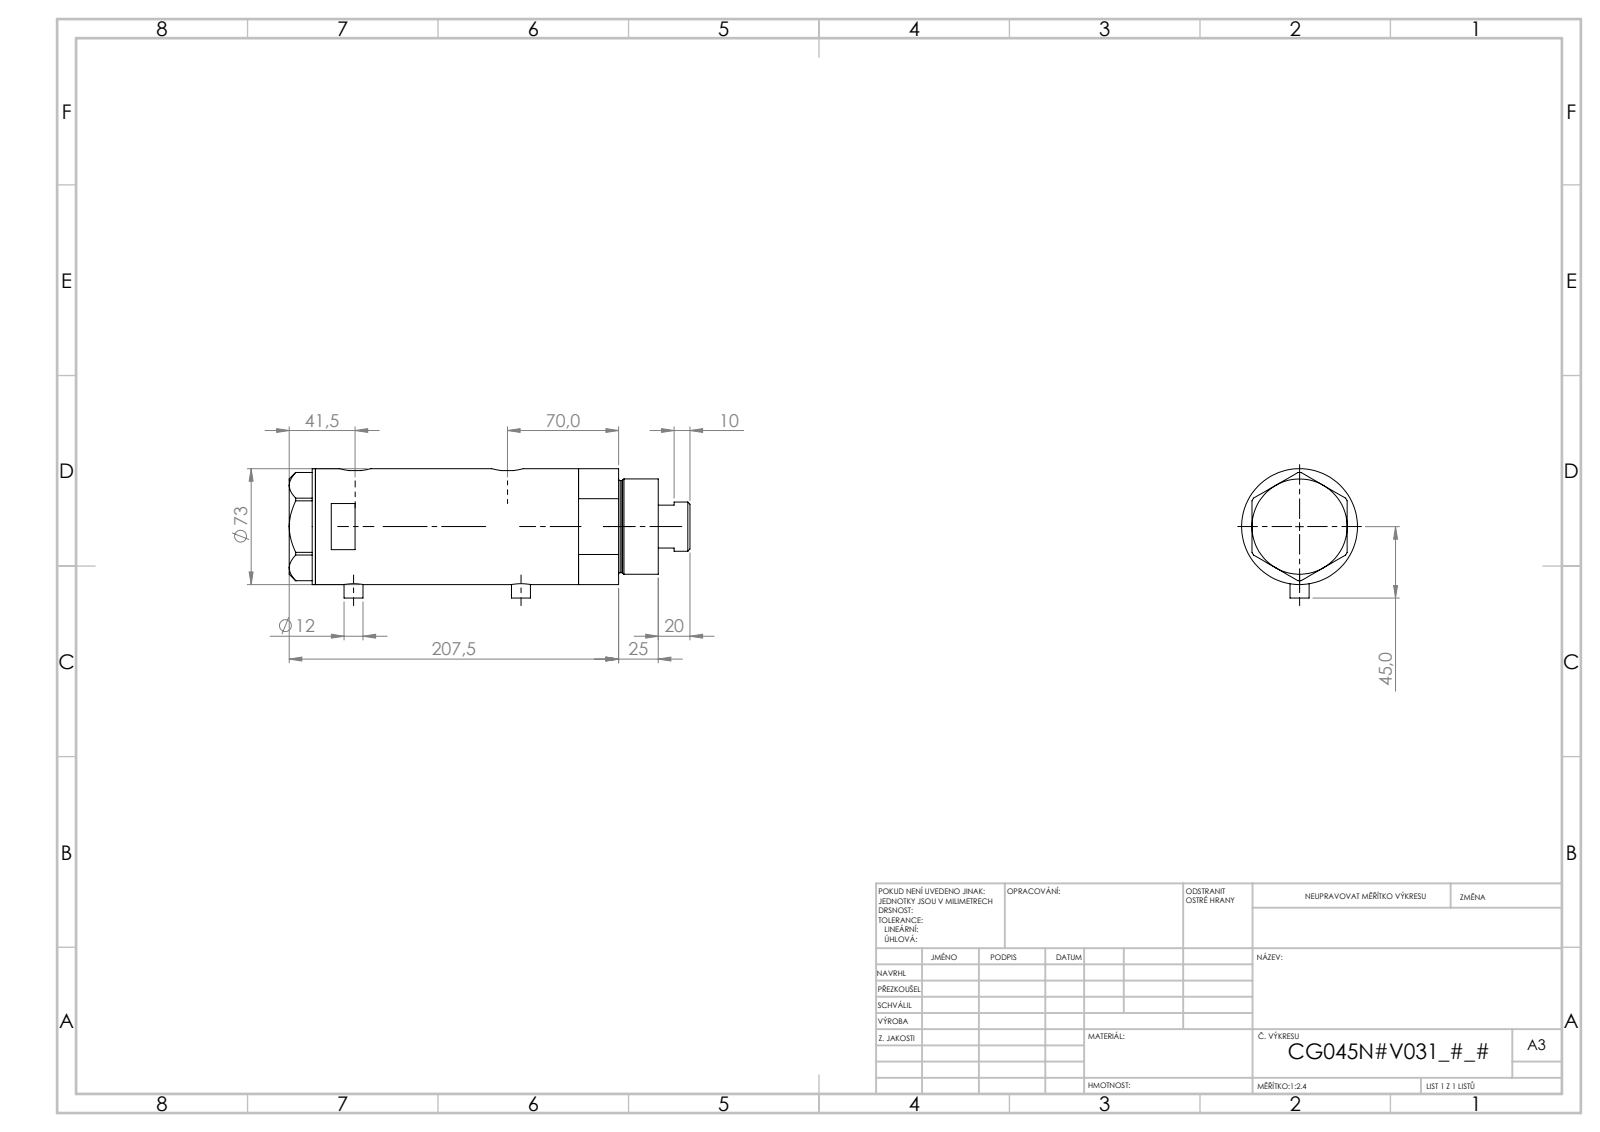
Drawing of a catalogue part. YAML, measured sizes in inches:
part_name: "V270CG_VC; V270CG_MIDDLE; V270CG_FRONT; V270CG_BACK"
step_written_by: "SolidWorks 2019 (CONFIG_CONTROL_DESIGN)"
units: inches
bodies: {solids: 4, faces: 120, planar: 49, cylindrical: 51, other: 20}
overall_size: [9.941, 3.209, 2.874]
volume: 54.8
surface_area: 231.8
round_holes:
  - {diameter: 0.492, count: 2}
  - {diameter: 0.518, count: 2}
  - {diameter: 0.413, count: 1}
  - {diameter: 1.26, count: 1}
  - {diameter: 1.319, count: 1}
  - {diameter: 1.772, count: 1}
  - {diameter: 1.89, count: 1}
  - {diameter: 2.52, count: 1}
round_bosses_or_shafts:
  - {diameter: 0.472, count: 2}
  - {diameter: 2.874, count: 1}
  - {diameter: 2.362, count: 1}
  - {diameter: 2.283, count: 1}
  - {diameter: 1.22, count: 1}
partial_cylinders:
  - {radius: 0.394, count: 2}
face_to_face_distances: [3.74, 4.764, 1.024, 0.65, 1.673, 5.413, 2.362, 0.079, 8.504, 9.154]
hole_center_spacings: [0.039, 0.335, 3.78, 3.819, 4.114, 4.154]
